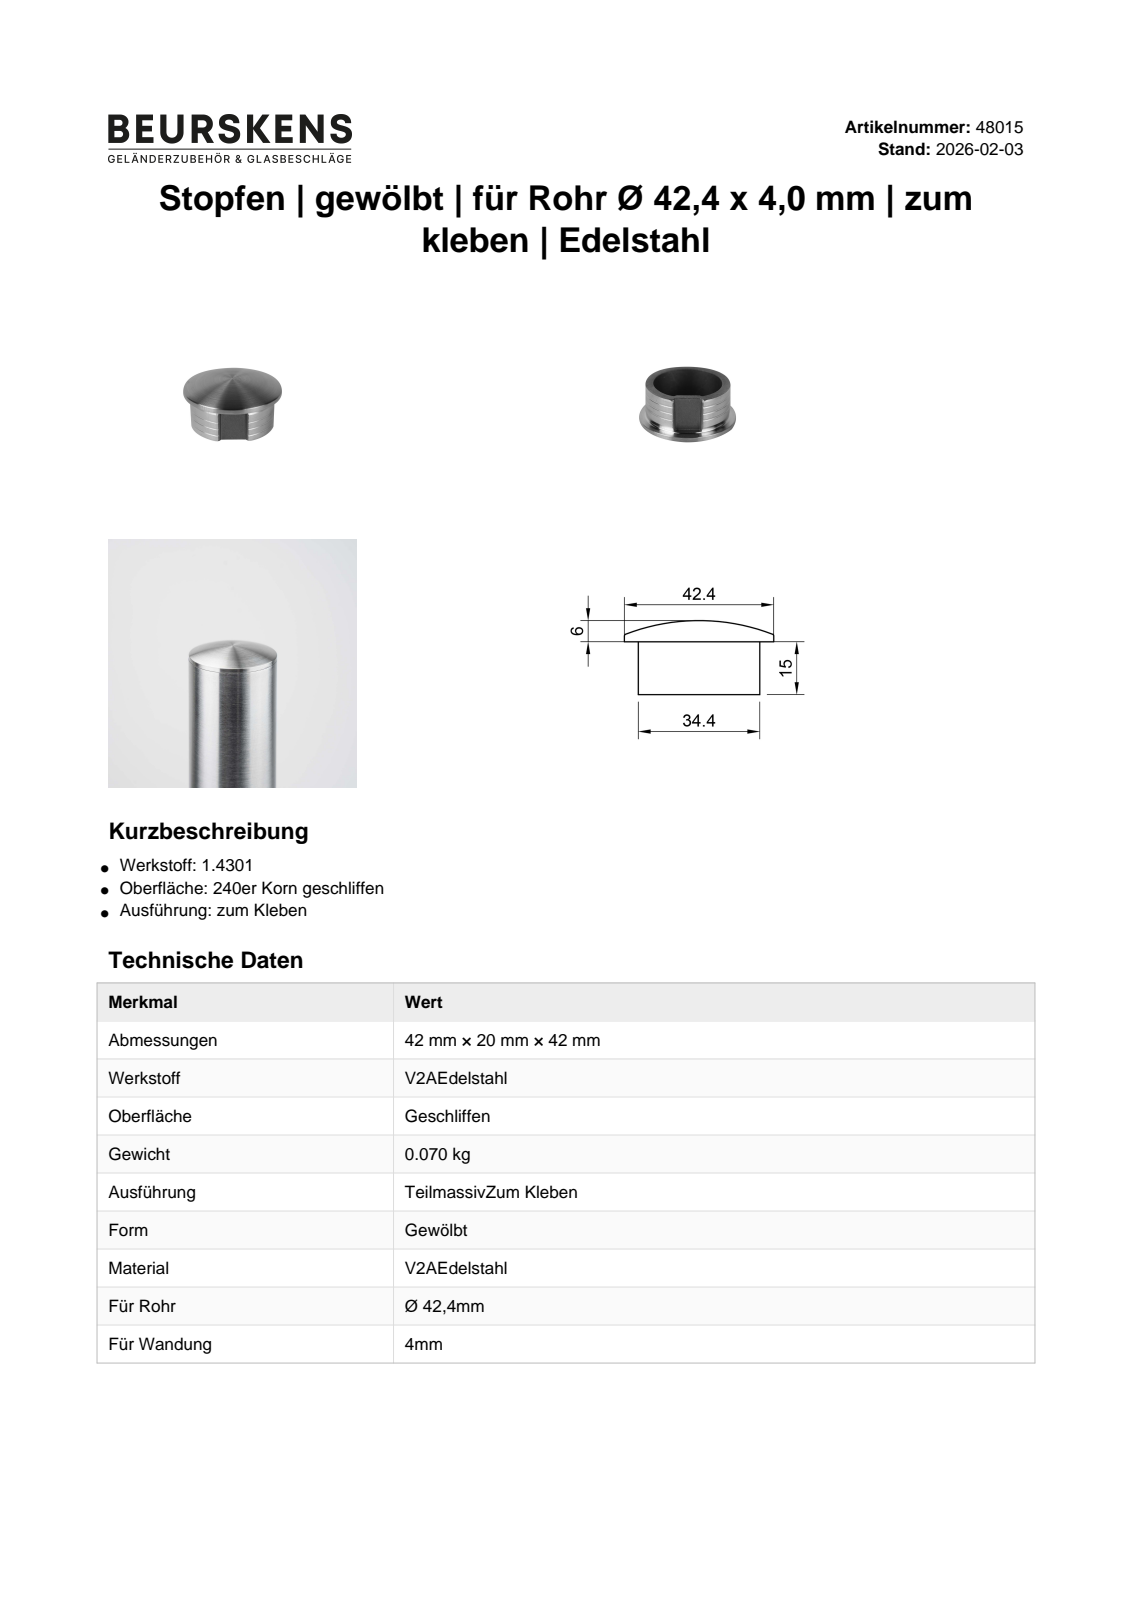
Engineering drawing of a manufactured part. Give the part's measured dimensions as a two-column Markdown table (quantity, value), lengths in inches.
| quantity | value |
| --- | --- |
| part name | 48015 |
| STEP written by | Autodesk Inventor 2022 (AUTOMOTIVE_DESIGN) |
| units | inches |
| bodies | 1 solid, 12 faces (4 planar, 4 cylindrical, 4 other) |
| overall size | 1.669 × 1.669 × 0.827 |
| volume | 0.403 in³ |
| surface area | 10.67 in² |
| round holes (diameter × count) | 1.142 × 1, 1.354 × 1 |
| round bosses / shafts (diameter × count) | 1.669 × 1, 1.358 × 1 |
| main face-to-face distances | 0.591 |
